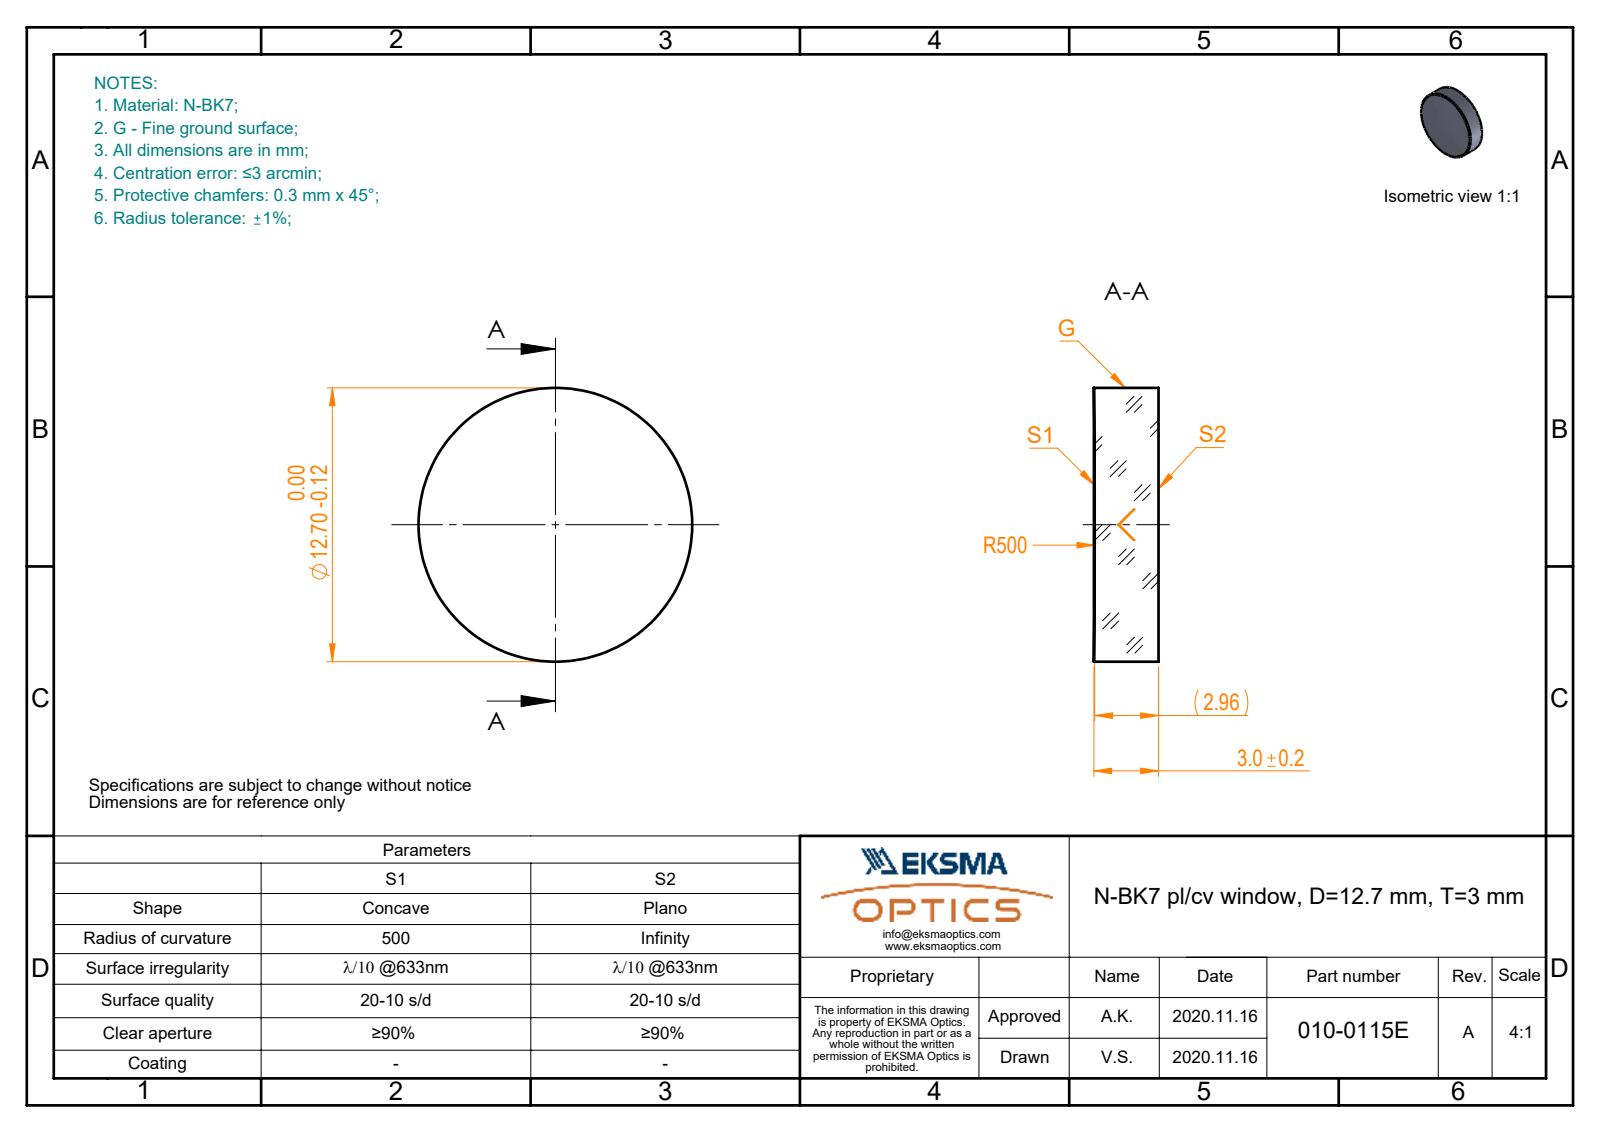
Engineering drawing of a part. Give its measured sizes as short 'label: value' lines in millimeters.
name: 010-0115E_N-BK7_PCV_window
written by: SolidWorks 2019 (CONFIG_CONTROL_DESIGN)
unit: mm
bodies: 1 solid, 5 faces (1 planar, 2 cylindrical, 2 other)
size: 12.7 × 12.7 × 3
volume: 377 mm³; area: 373 mm²
bosses: 1× ⌀12.7
